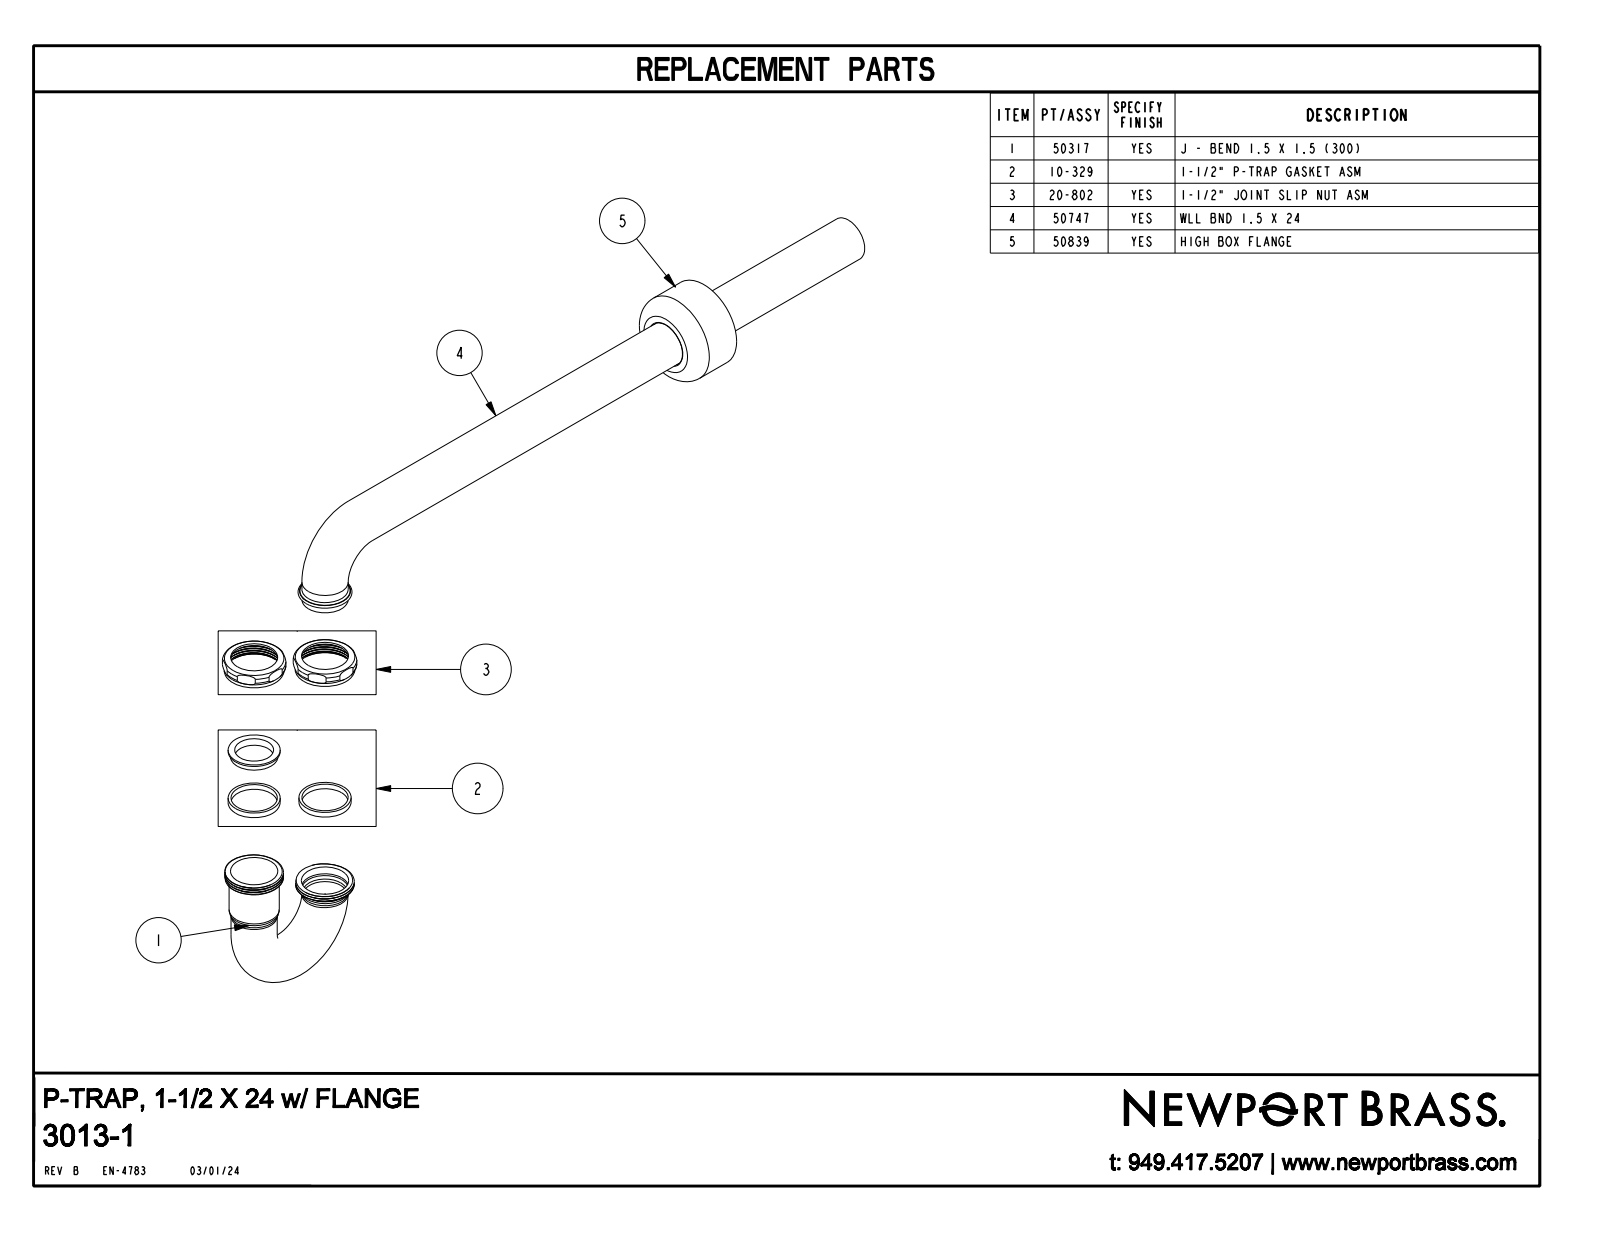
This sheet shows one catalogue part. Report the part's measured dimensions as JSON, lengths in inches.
{"part_name": "3013-1", "step_written_by": "CREO PARAMETRIC BY PTC INC, 2018500 (CONFIG_CONTROL_DESIGN)", "units": "inches", "bodies": {"solids": 3, "faces": 255, "planar": 49, "cylindrical": 109, "other": 97}, "overall_size": [28.28, 6.623, 3], "volume_in3": 36.1, "surface_area_in2": 459.3, "round_holes": [[1.406, 2], [1.52, 2], [1.78, 2], [1.256, 1], [1.51, 1], [2.954, 1]], "round_bosses_or_shafts": [[1.5, 3], [1.94, 2], [1.625, 2], [3, 1], [1.883, 1], [1.715, 1], [1.69, 1], [1.556, 1]], "partial_cylinders_radius": [[0.939, 2], [1.03, 2], [0.862, 1]], "face_to_face_distances": [0.5, 1.97, 2, 0.25, 2.5, 2.31, 15.875, 2.815, 0.227, 15.648], "hole_center_spacings": [3.25]}
